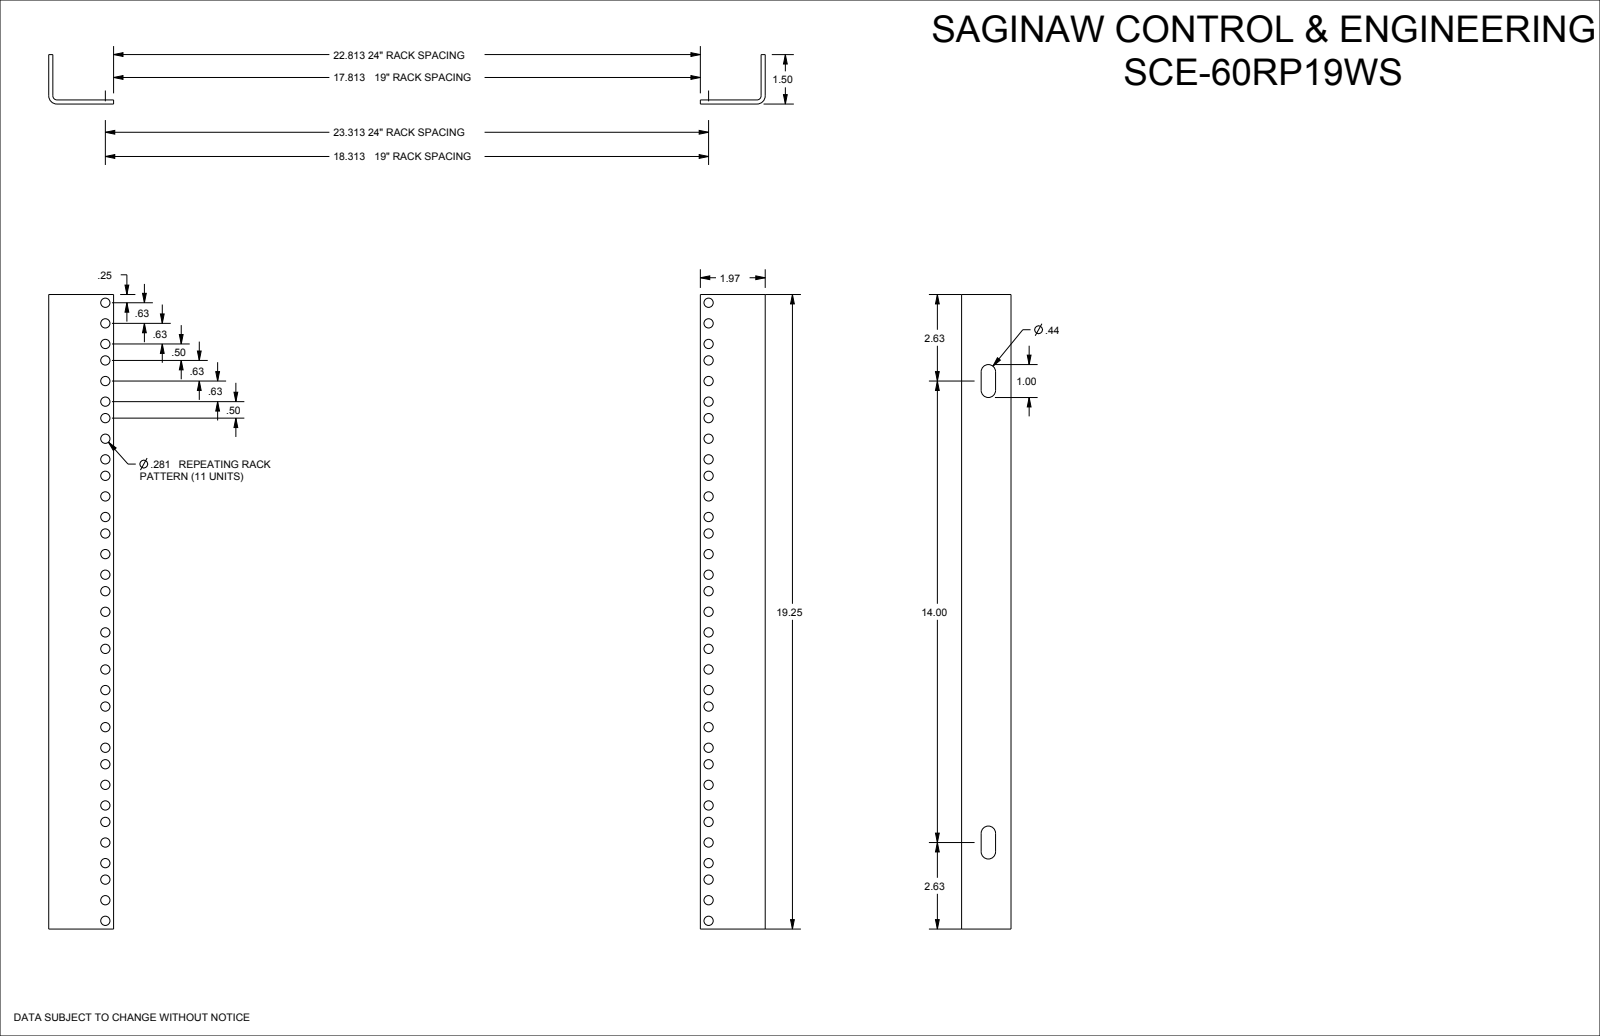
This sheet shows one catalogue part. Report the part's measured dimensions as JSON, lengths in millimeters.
{"part_name": "SCE-60RP19WS", "step_written_by": "SolidWorks 2019 (CONFIG_CONTROL_DESIGN)", "units": "millimeters", "bodies": {"solids": 2, "faces": 102, "planar": 24, "cylindrical": 78, "other": 0}, "overall_size": [679.5, 489, 38.1], "volume_mm3": 245800, "surface_area_mm2": 167500, "round_holes": [[7.1, 66]], "partial_cylinders_radius": [[5.6, 4], [3.2, 2], [6.4, 2]], "face_to_face_distances": [3.2, 676.3, 679.5, 673.1, 676.3, 3.2, 38.1, 34.9, 50, 629.4], "hole_center_spacings": [44.5, 88.9, 133.4, 177.8, 222.3, 15.9, 15.9, 31.8]}
